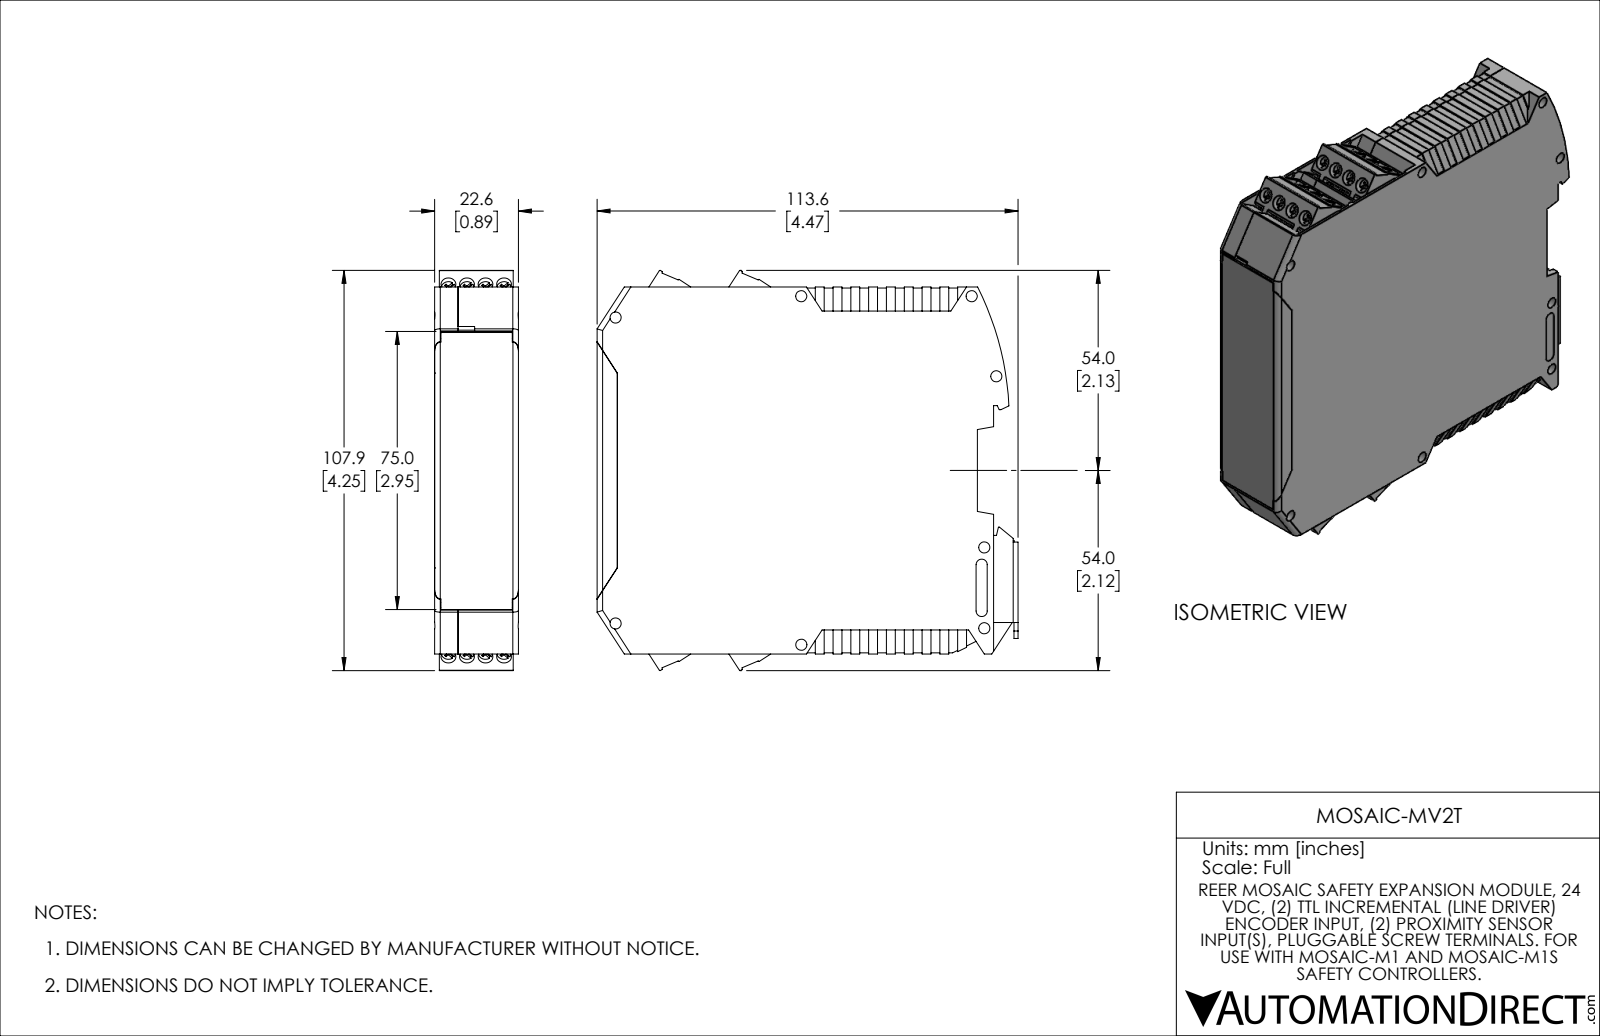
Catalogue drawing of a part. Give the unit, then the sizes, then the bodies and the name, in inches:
Units: inches
Overall size (bounding box): 4.472 × 4.25 × 0.89
Round holes (diameter × count): ⌀0.055 ×18, ⌀0.11 ×16, ⌀0.157 ×16, ⌀0.118 ×14, ⌀0.063 ×1
Round bosses / shafts (diameter × count): ⌀0.149 ×16, ⌀0.177 ×1, ⌀0.11 ×1, ⌀0.053 ×1
Partial cylindrical surfaces — rounded edges, fillets, slot ends (radius × count): R0.012 ×33, R0.114 ×16, R0.008 ×12, R0.03 ×12, R0.059 ×8, R0.031 ×6, R0.098 ×5, R0.024 ×4
Main face-to-face distances: 0.049, 0.841, 0.89, 0.791, 0.039, 0.248, 0.047, 0.199, 0.593, 0.642
Hole centre spacings: 0.197, 0.394, 0.591, 0.503, 0.504, 0.74, 0.74, 0.463
Volume: 3.484 in³ · Surface area: 117.5 in²
Bodies: 9 solids, 1954 faces (1569 planar, 379 cylindrical, 6 other)
Part name (STEP PRODUCT): MOSAIC-MV2T
STEP written by: SolidWorks 2021 (AUTOMOTIVE_DESIGN)
